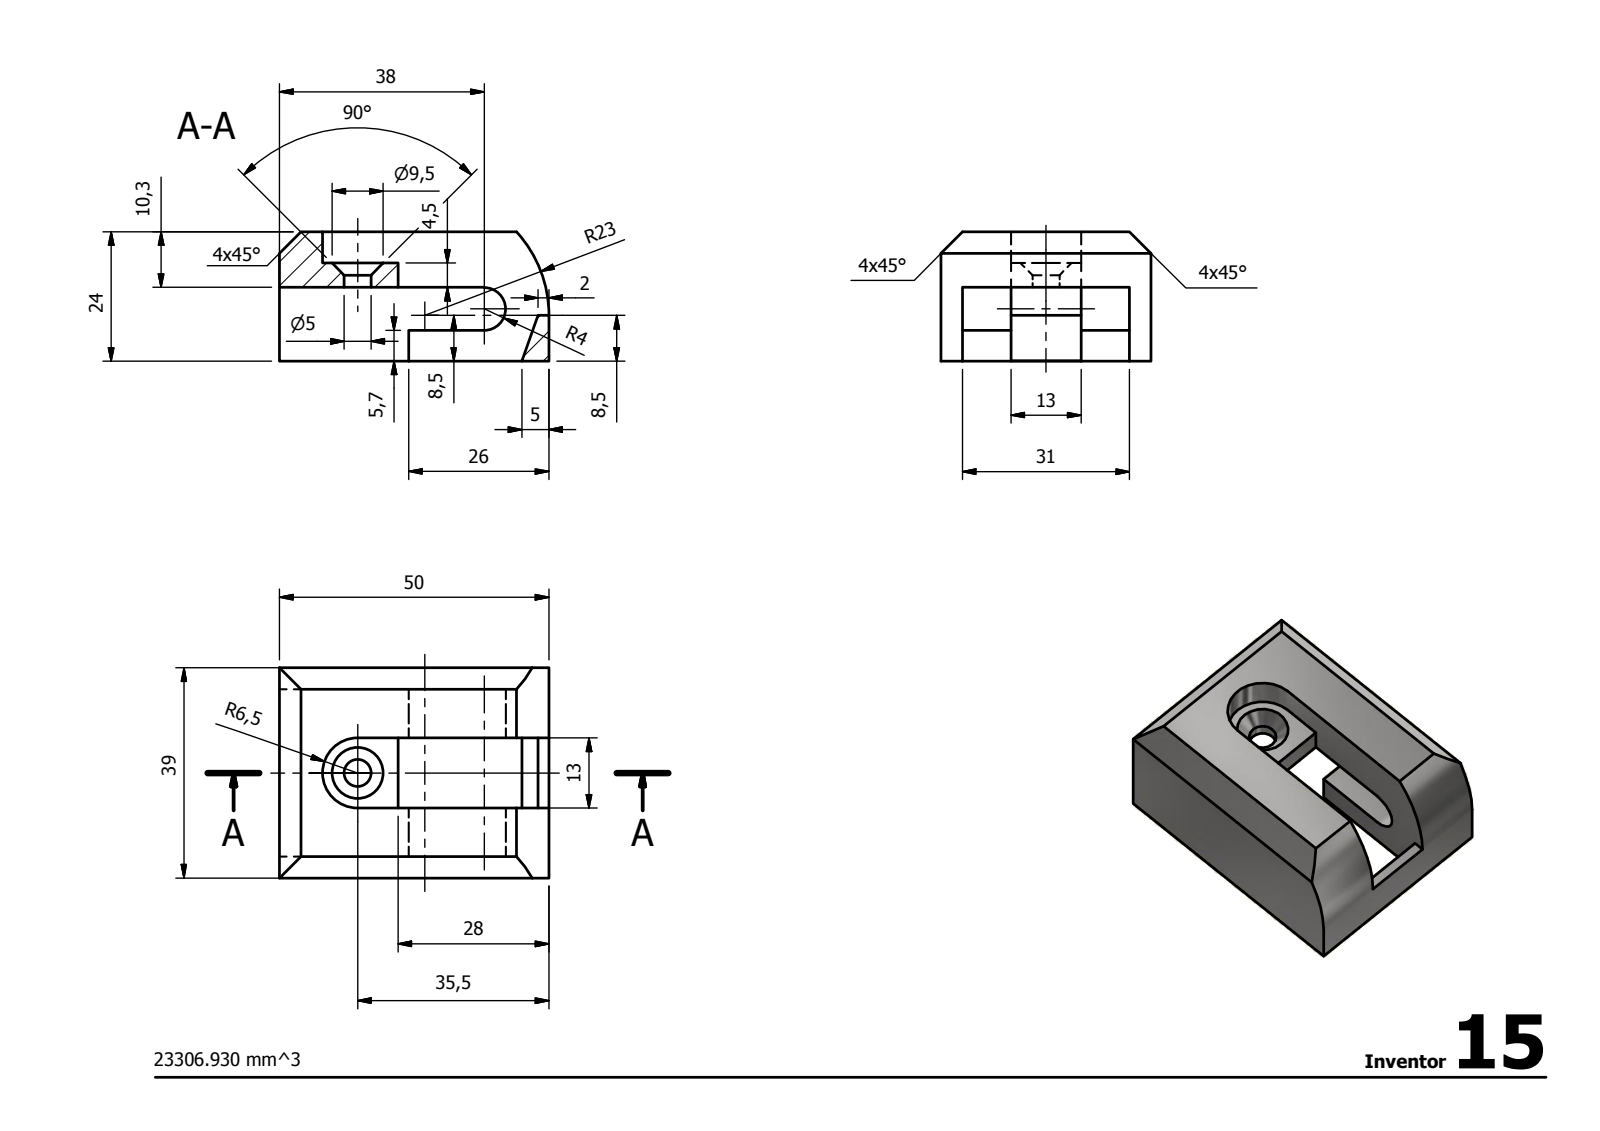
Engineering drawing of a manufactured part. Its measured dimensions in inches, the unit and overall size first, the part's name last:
Units: inches
Overall size (bounding box): 1.969 × 1.535 × 0.945
Round holes (diameter × count): ⌀0.197 ×1
Partial cylindrical surfaces — rounded edges, fillets, slot ends (radius × count): R0.157 ×1, R0.256 ×1, R0.906 ×1
Main face-to-face distances: 0.512, 1.024, 0.866, 1.535, 0.539, 0.157, 1.378, 0.354, 0.945, 0.406
Volume: 1.422 in³ · Surface area: 14.67 in²
Bodies: 1 solid, 30 faces (23 planar, 6 cylindrical, 1 other)
STEP written by: Autodesk Inventor 2014 (AUTOMOTIVE_DESIGN)
